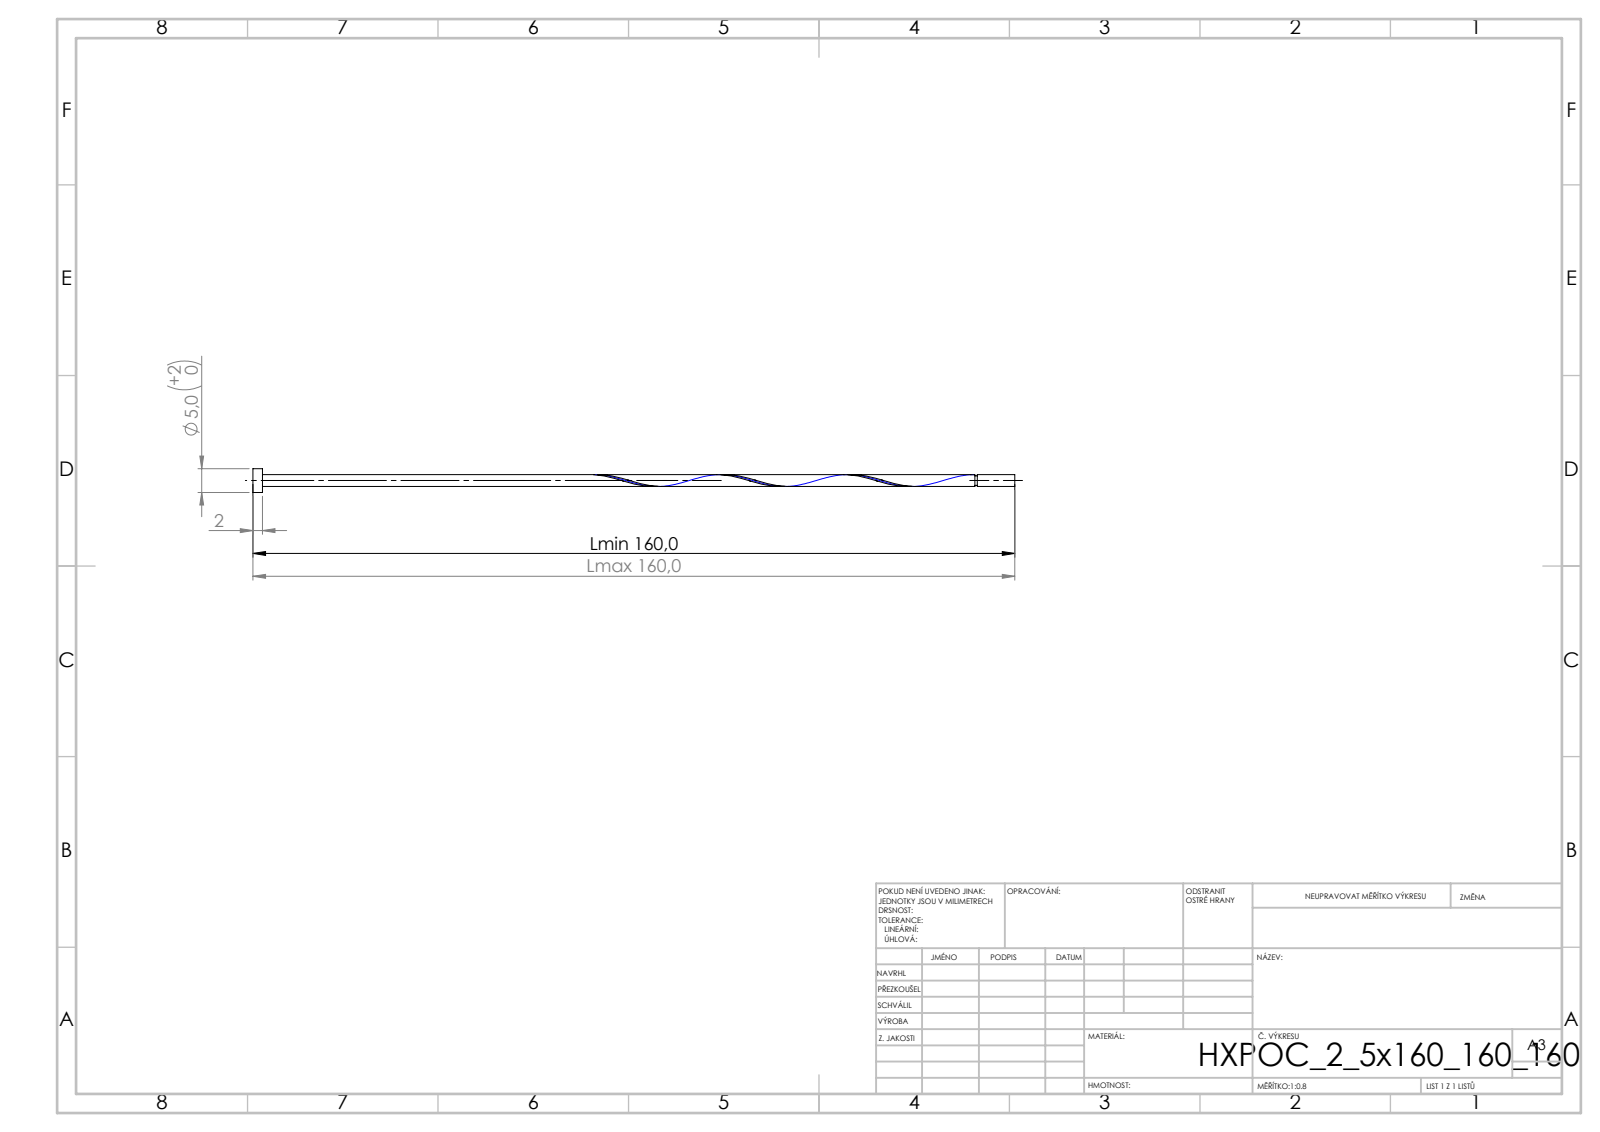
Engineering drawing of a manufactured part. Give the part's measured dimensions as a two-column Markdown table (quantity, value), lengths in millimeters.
| quantity | value |
| --- | --- |
| STEP written by | SolidWorks 2019 (CONFIG_CONTROL_DESIGN) |
| units | millimeters |
| bodies | 1 solid, 16 faces (6 planar, 9 cylindrical, 1 other) |
| overall size | 160 × 5 × 5 |
| volume | 981 mm³ |
| surface area | 1 753 mm² |
| round bosses / shafts (diameter × count) | 5 × 1, 2.5 × 1, 2 × 1 |
| main face-to-face distances | 2, 160, 158, 152.11, 150.11, 7.89, 151.61, 149.61, 0.5, 8.39 |
